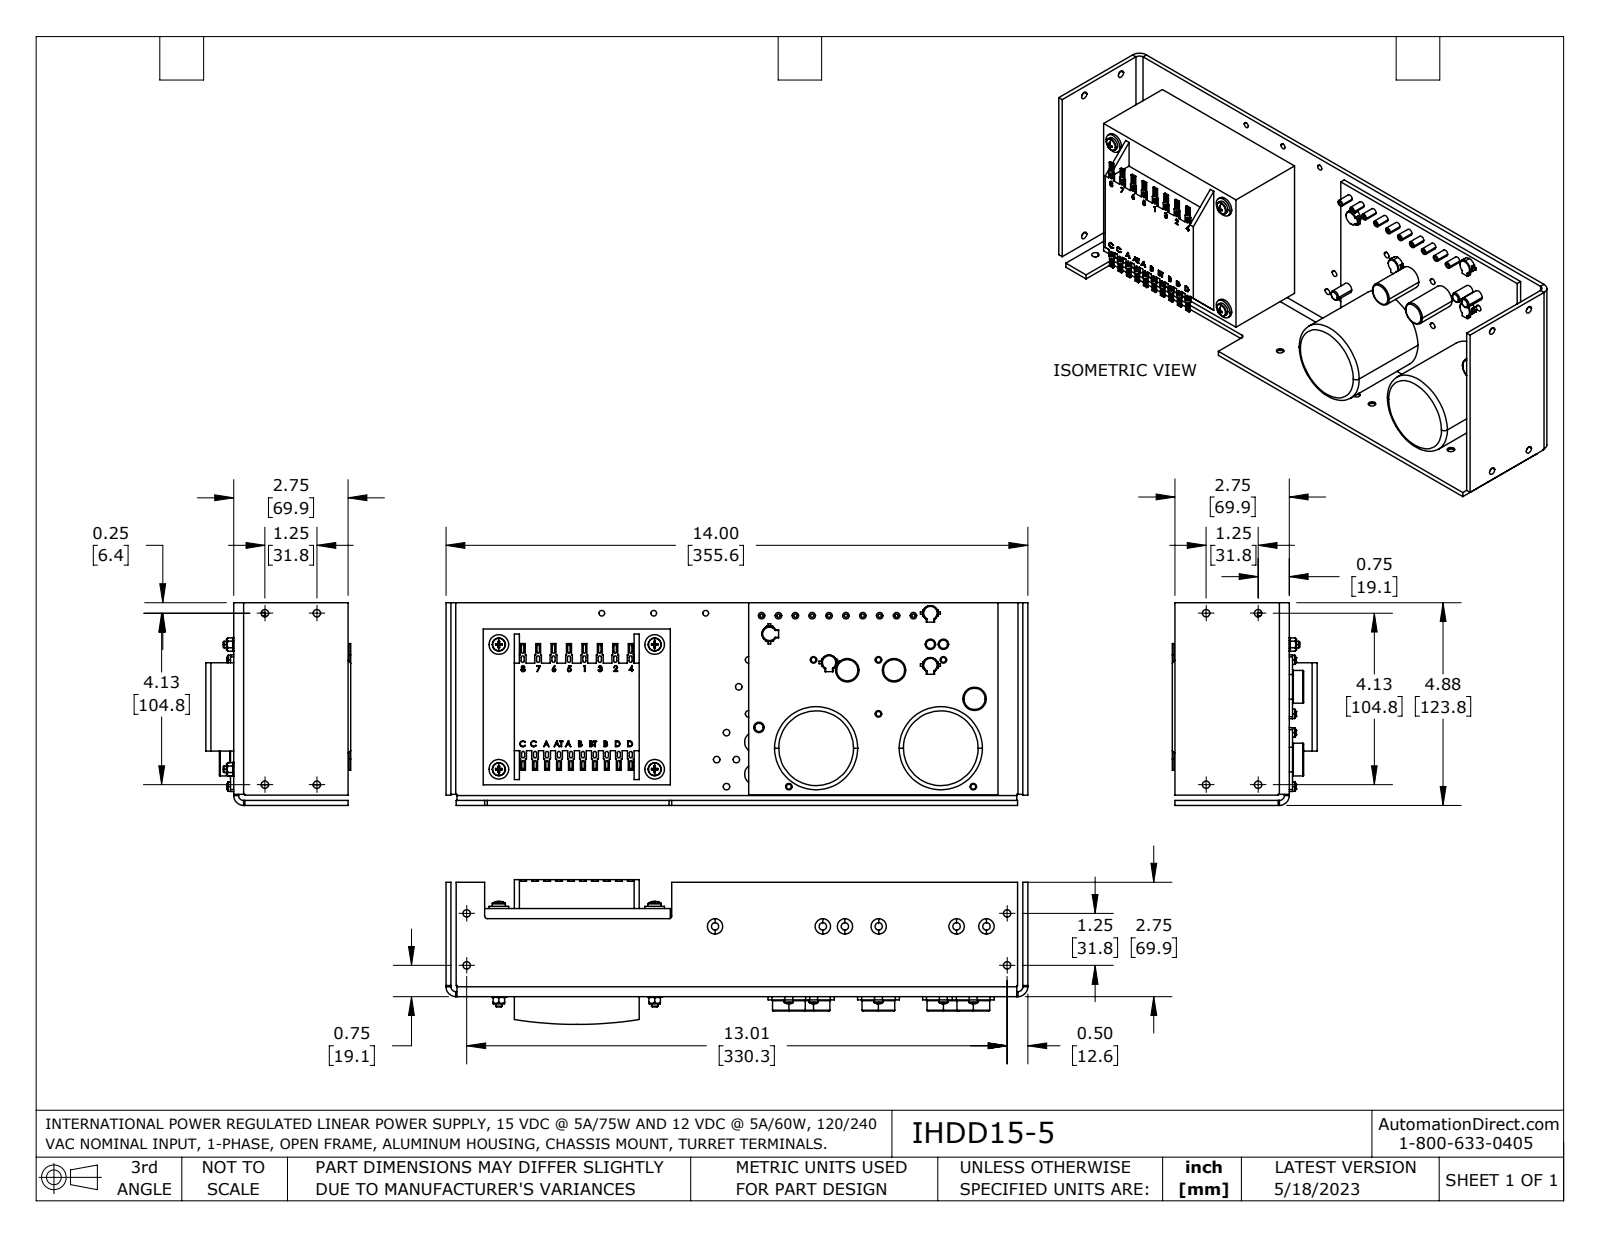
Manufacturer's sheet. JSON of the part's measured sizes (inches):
{"part_name": "IHDD15-5", "step_written_by": "SolidWorks 2023 (AUTOMOTIVE_DESIGN)", "units": "inches", "bodies": {"solids": 29, "faces": 2102, "planar": 1210, "cylindrical": 571, "other": 321}, "overall_size": [14, 4.875, 3.484], "volume_in3": 75.03, "surface_area_in2": 435.4, "round_holes": [[0.157, 26], [0.177, 26], [0.079, 10], [0.502, 6], [0.169, 4], [0.192, 4], [0.138, 3]], "round_bosses_or_shafts": [[0.157, 18], [0.236, 10], [0.22, 10], [0.118, 10], [0.787, 5], [0.472, 4], [0.315, 4], [0.276, 4]], "partial_cylinders_radius": [[0.029, 36], [0.037, 36], [0.062, 6], [0.502, 5], [0.126, 4], [0.167, 4], [0.118, 3], [0.236, 3]], "face_to_face_distances": [0.118, 0.315, 0.197, 13.882, 0.433, 3.75, 14, 13.764, 1.685, 1.803], "hole_center_spacings": [0.406, 1.624, 1.218, 1.25, 1.299, 0.812, 0.812, 1.563]}
